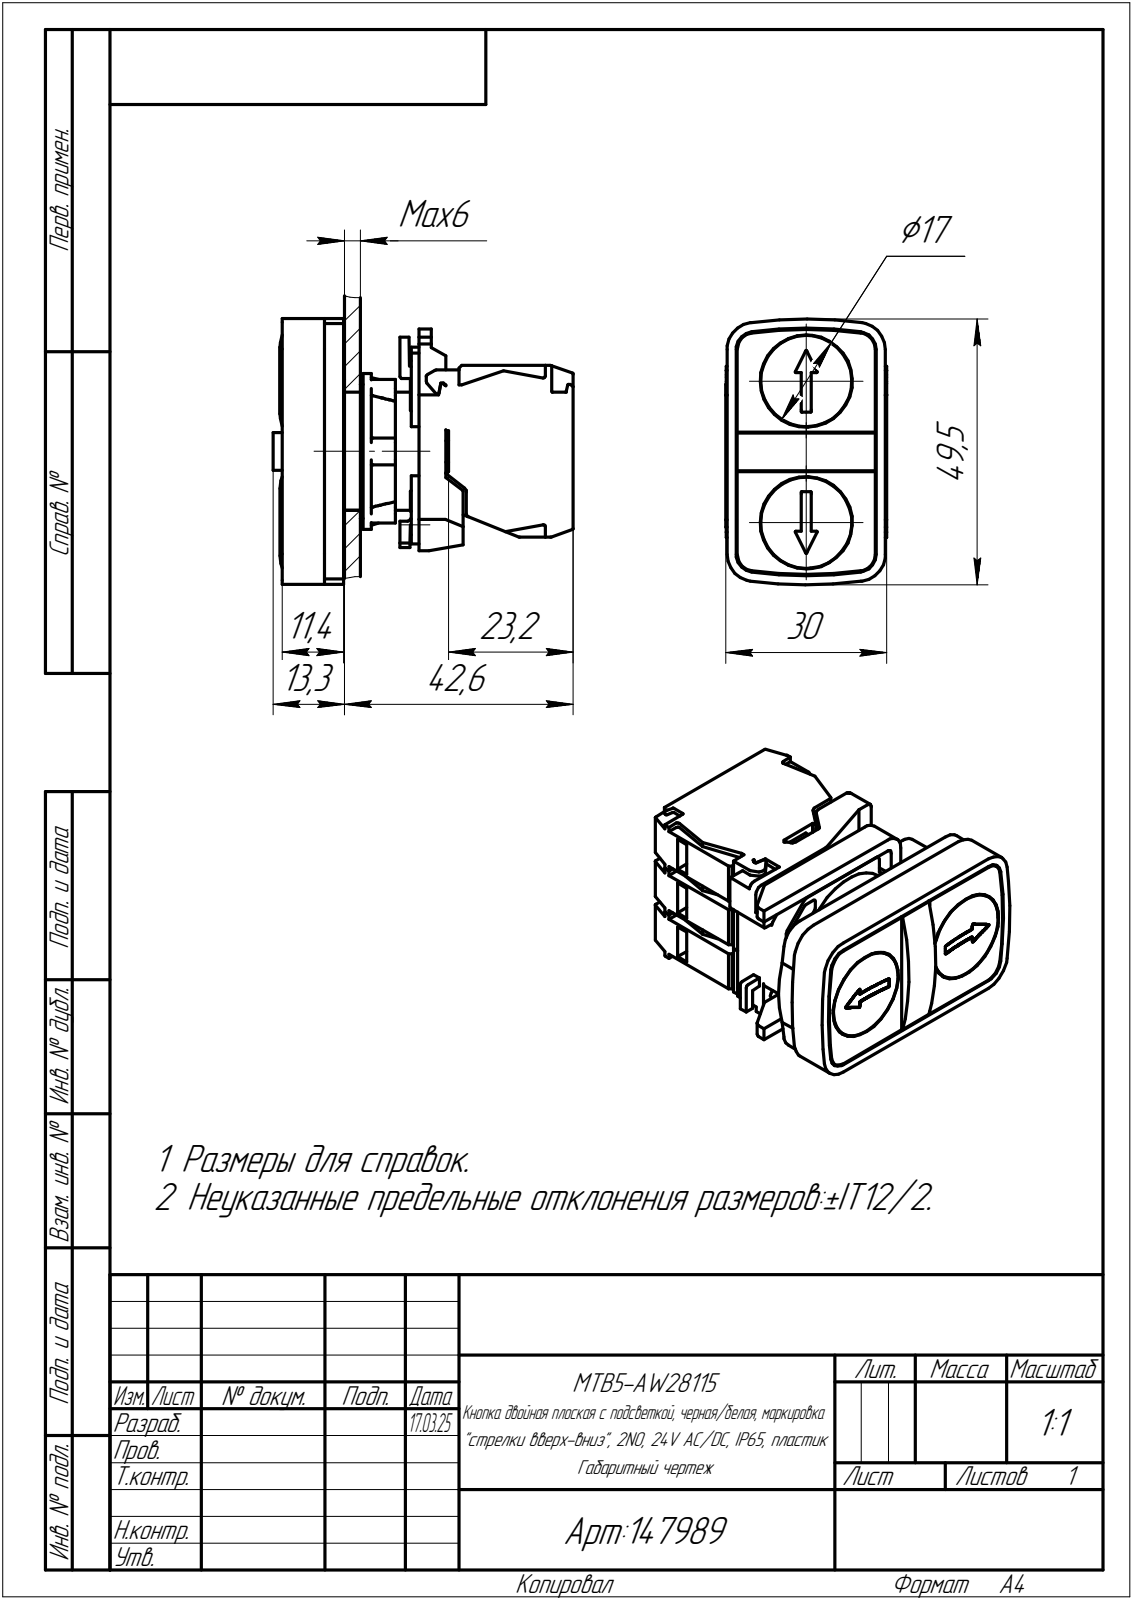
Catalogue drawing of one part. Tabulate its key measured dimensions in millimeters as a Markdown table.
| quantity | value |
| --- | --- |
| part name | MTB5-AW28115 |
| STEP written by | C3D Toolkit (CONFIG_CONTROL_DESIGN) |
| units | millimeters |
| bodies | 1 solid, 661 faces (451 planar, 187 cylindrical, 23 other) |
| overall size | 55.9 × 49.5 × 30 |
| volume | 47 731 mm³ |
| surface area | 19 405 mm² |
| round holes (diameter × count) | 6 × 2, 17.2 × 2, 5.2 × 1, 20.5 × 1 |
| round bosses / shafts (diameter × count) | 17 × 2, 29 × 1, 26.8 × 1, 25 × 1, 22 × 1 |
| partial cylindrical surfaces (radius × count) | 1 × 15, 0.2 × 13, 0.1 × 10, 0.5 × 7, 2.5 × 4, 3.1 × 4, 3.3 × 4, 4.35 × 4 |
| main face-to-face distances | 10, 9.9, 20, 19.9, 10.1, 14.1, 9, 25.5, 11.4, 19.1 |
| hole center spacings | 4.7, 8.5, 13.2, 21.7, 17, 26.4 |
